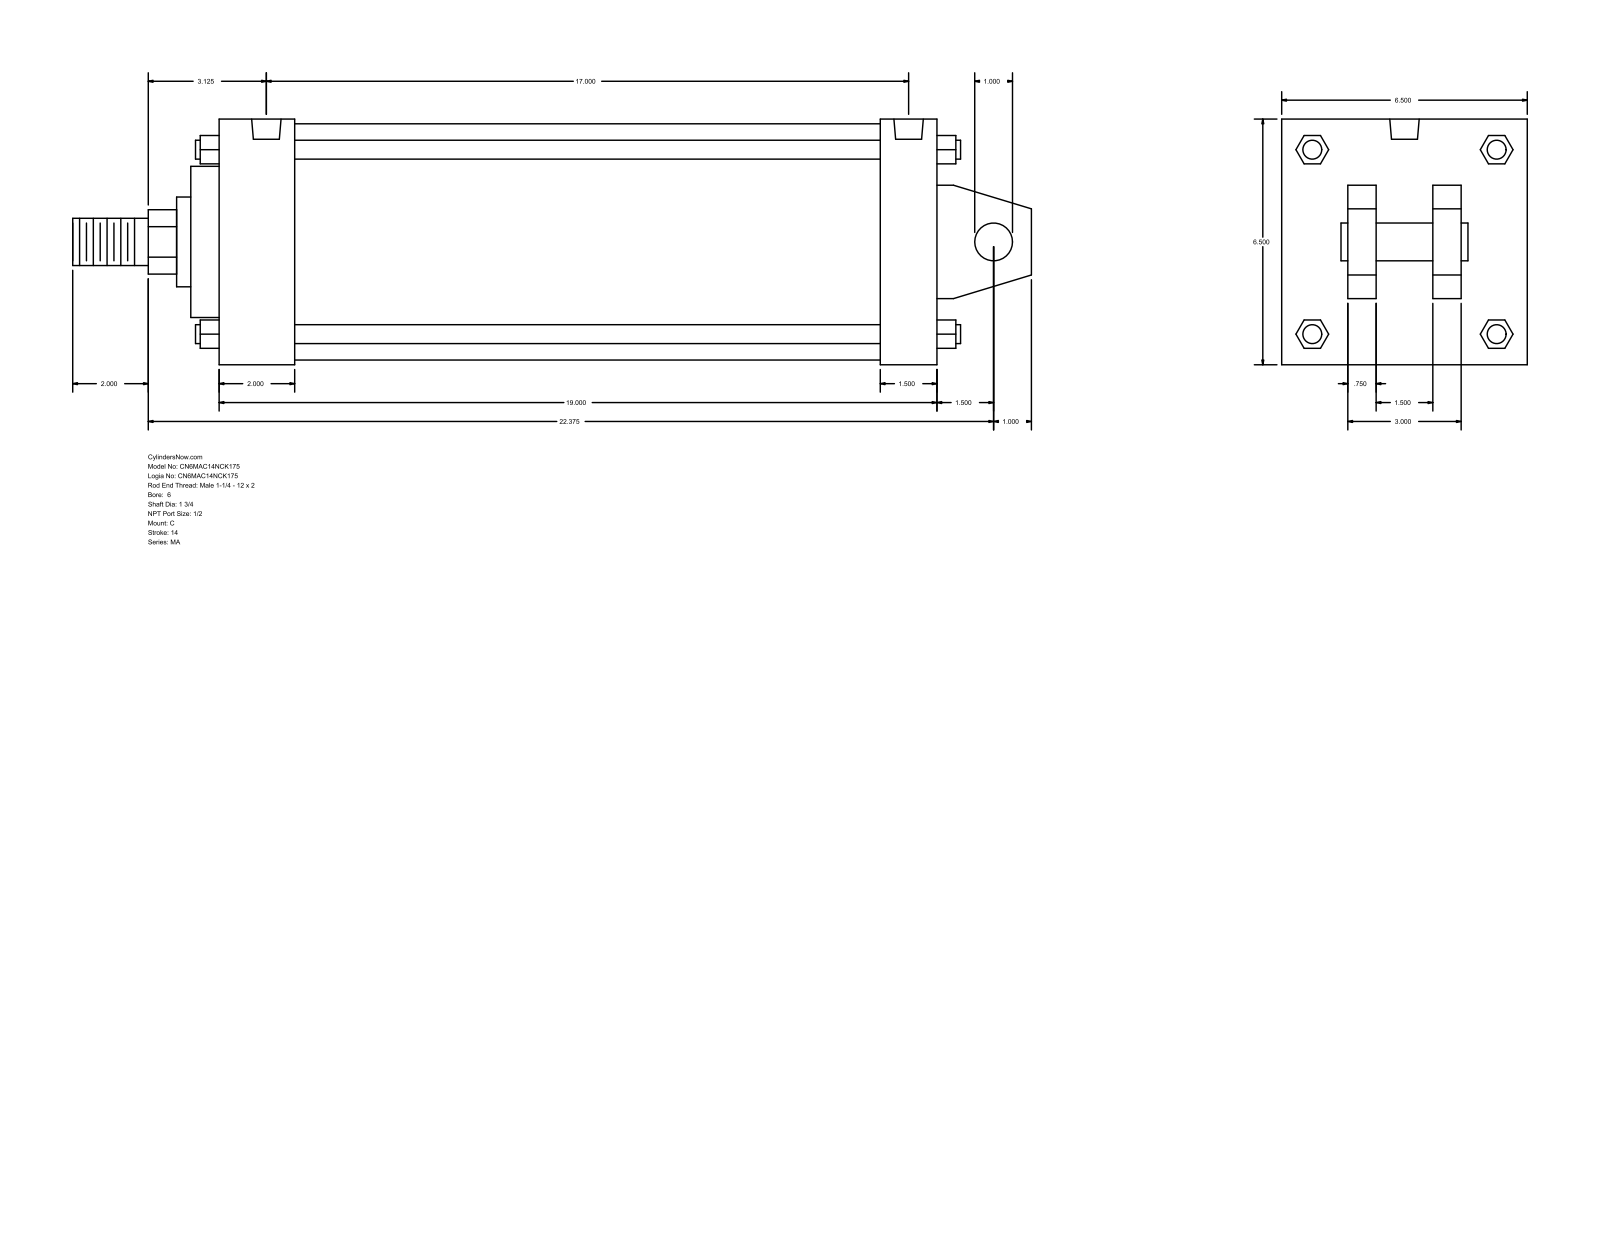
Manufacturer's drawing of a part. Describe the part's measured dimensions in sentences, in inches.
The part is named "MA_C__0600_1.75". Its 3-D file was written by "GSSL Pune (CONFIG_CONTROL_DESIGN)". It is 0 solids with 141 faces: 109 planar, 32 cylindrical and 0 other. Overall it measures 25.375 by 6.5 by 6.5 inches. Round holes: 4 of diameter 0.687, 2 of diameter 0.778. Round bosses or shafts: 4 of diameter 0.5, 1 of diameter 6.25, 1 of diameter 4, 1 of diameter 2.375, 1 of diameter 1.75, 1 of diameter 1.25, 1 of diameter 1. Partial cylindrical surfaces (rounded edges, fillets, slot ends): 1 of radius 0.852. The main face-to-face distances are 6.5, 19, 0.75, 2.5, 4, 2, 1.75, 4.75, 17.5, 2.25. The hole center spacings are 17.
